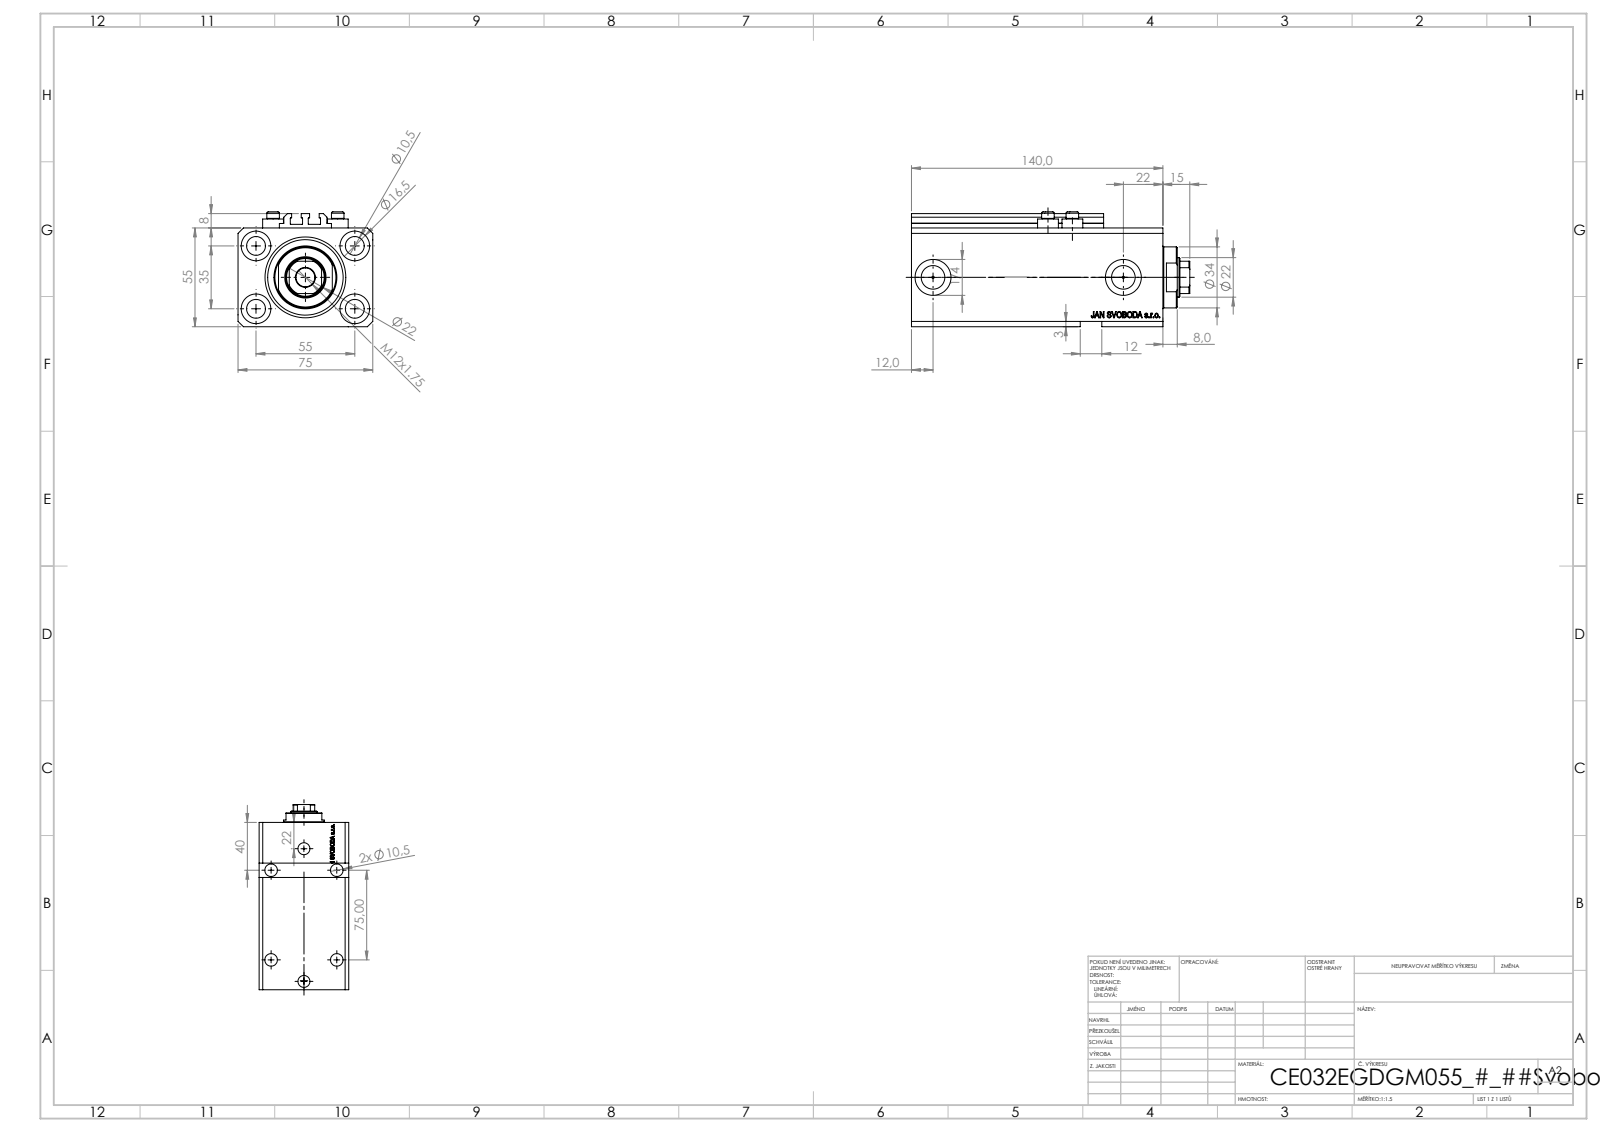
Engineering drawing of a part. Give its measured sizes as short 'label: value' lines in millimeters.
name: ALLEN BOLT V250CE; V250CE_C_VCP; V250CE_VC_E; V250CE_E_Body
written by: SolidWorks 2019 (CONFIG_CONTROL_DESIGN)
unit: mm
bodies: 8 solids, 1100 faces (518 planar, 158 cylindrical, 424 other)
size: 155 × 75 × 64
volume: 481 599 mm³; area: 116 451 mm²
holes: 9× ⌀10.5, 4× ⌀1.25, 4× ⌀4, 4× ⌀16.5, 2× ⌀10, 2× ⌀13.16, 2× ⌀20, 1× ⌀22, 1× ⌀32, 1× ⌀45
bosses: 4× ⌀11.6, 4× ⌀7, 1× ⌀34
rounds: 10× R0.2, 1× R10.5
face distances: 55, 75, 15, 9.9, 140, 125, 3, 57, 115.1, 130.1
hole spacings: 32.6, 32.87, 55, 96.98, 13.6, 14.09, 25.81, 32.58
